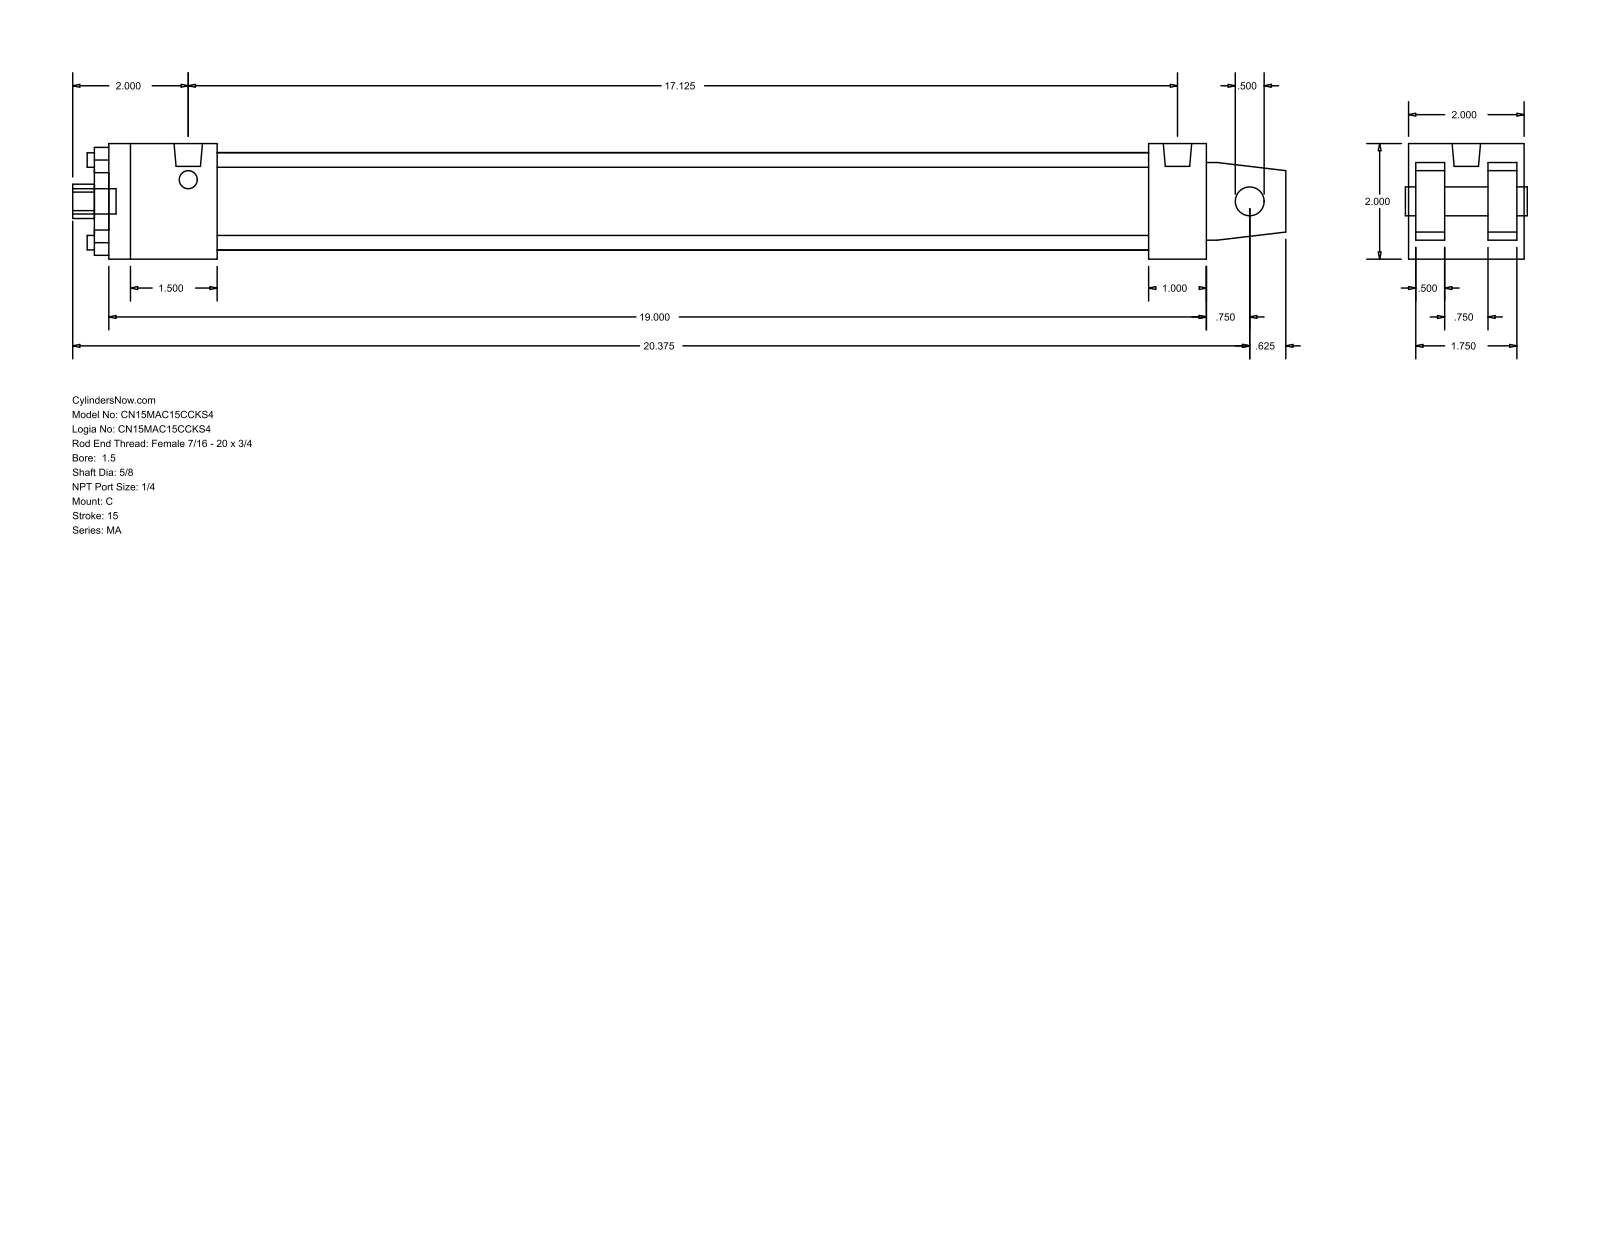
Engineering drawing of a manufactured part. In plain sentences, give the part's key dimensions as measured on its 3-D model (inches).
The part is named "MA_C__0150_0.625". Its 3-D file was written by "GSSL Pune (CONFIG_CONTROL_DESIGN)". It is 0 solids with 103 faces: 76 planar, 27 cylindrical and 0 other. Overall it measures 21 by 2 by 2 inches. Round holes: 4 of diameter 0.25, 1 of diameter 0.5, 1 of diameter 0.625, 1 of diameter 1.125, 1 of diameter 1.69. Round bosses or shafts: 4 of diameter 0.313, 2 of diameter 0.492, 1 of diameter 0.437. Partial cylindrical surfaces (rounded edges, fillets, slot ends): 1 of radius 0.297. The main face-to-face distances are 2, 0.5, 0.125, 0.625, 1.375, 1.875, 1.25, 19, 18, 1. The hole center spacings are 1.011, 1.43, 2.022.
